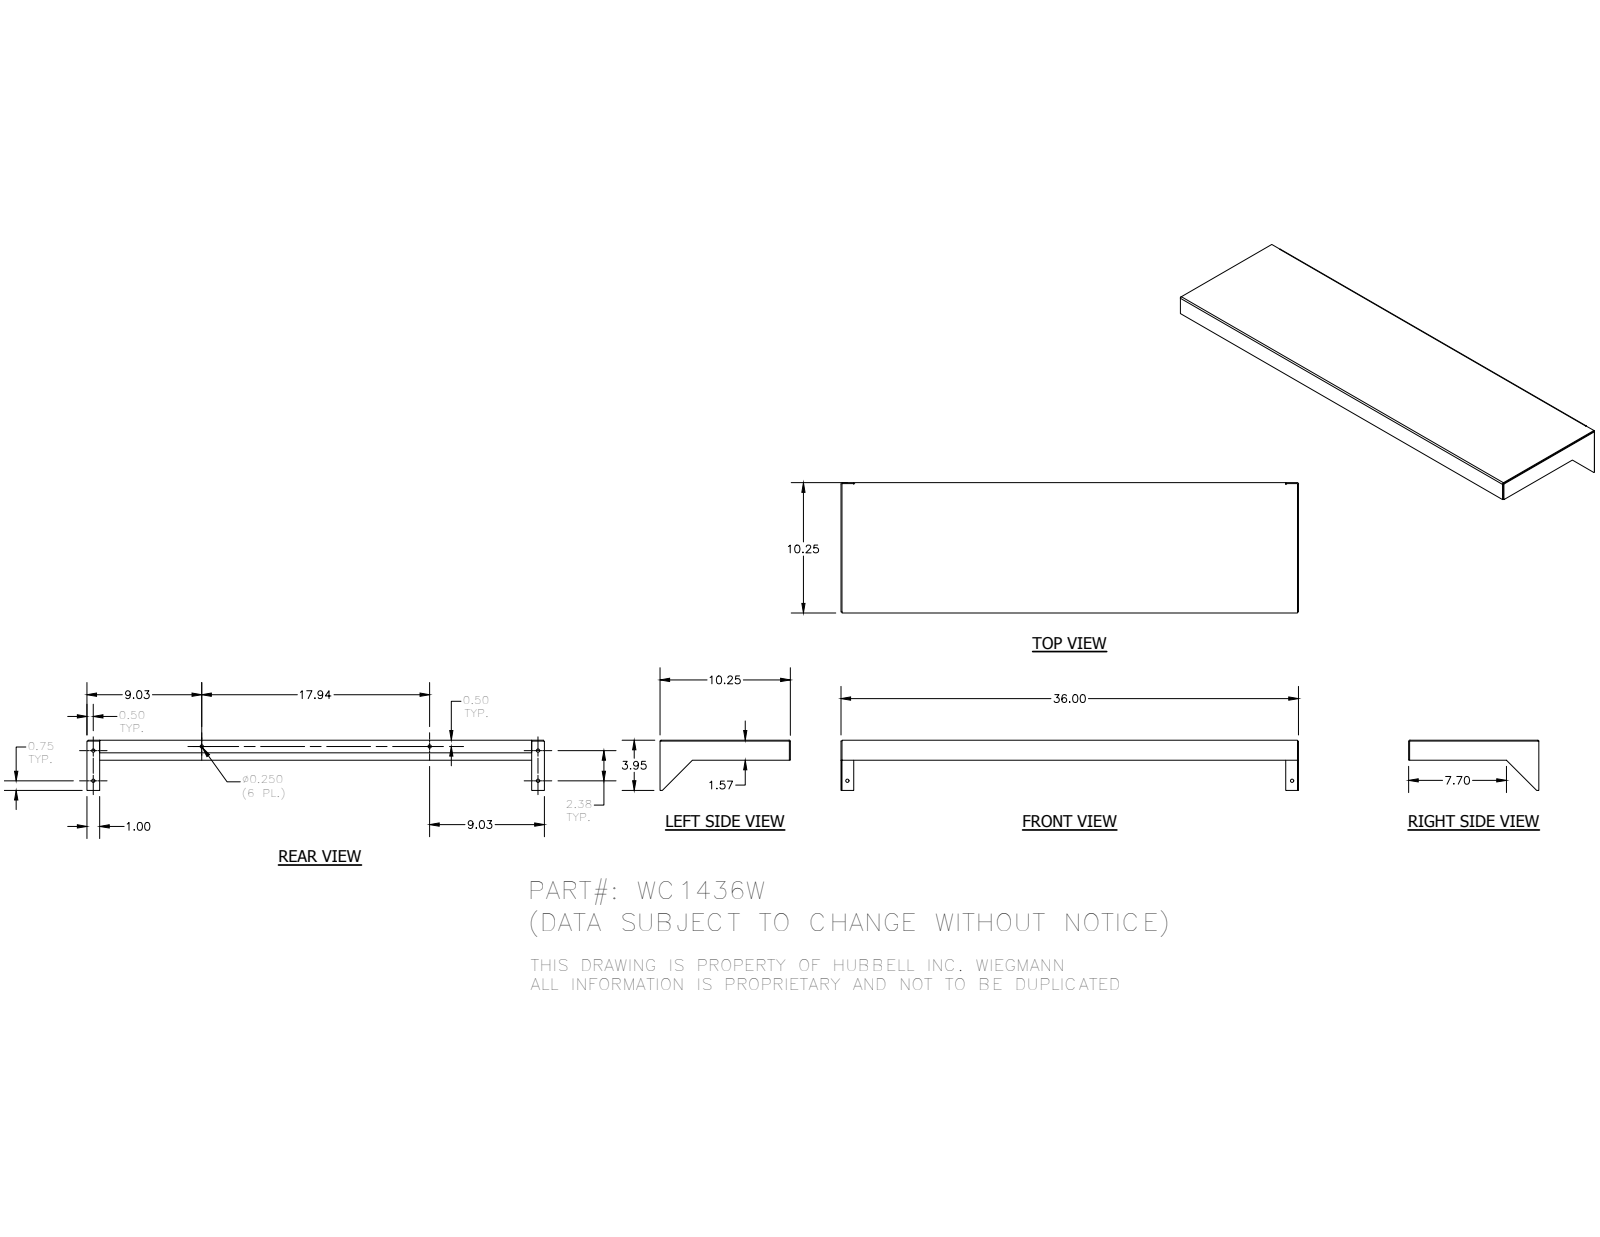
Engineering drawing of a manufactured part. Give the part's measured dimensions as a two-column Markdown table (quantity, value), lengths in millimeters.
| quantity | value |
| --- | --- |
| part name | WC1436WBKP; WC14WRS; WC14WLS; WC14W |
| STEP written by | Autodesk Inventor 2016 (AUTOMOTIVE_DESIGN) |
| units | millimeters |
| bodies | 3 solids, 68 faces (54 planar, 14 cylindrical, 0 other) |
| overall size | 914.4 × 260.35 × 100.31 |
| volume | 599 314 mm³ |
| surface area | 645 284 mm² |
| round holes (diameter × count) | 6.35 × 6 |
| partial cylindrical surfaces (radius × count) | 0.79 × 4, 2.67 × 4 |
| main face-to-face distances | 1.88, 258.47, 256.59, 260.35, 912.52, 910.64, 914.4, 39.98, 38.1, 25.4 |
| hole center spacings | 60.33, 889, 891.04, 216.84, 216.85, 227.27, 227.28, 455.63 |
